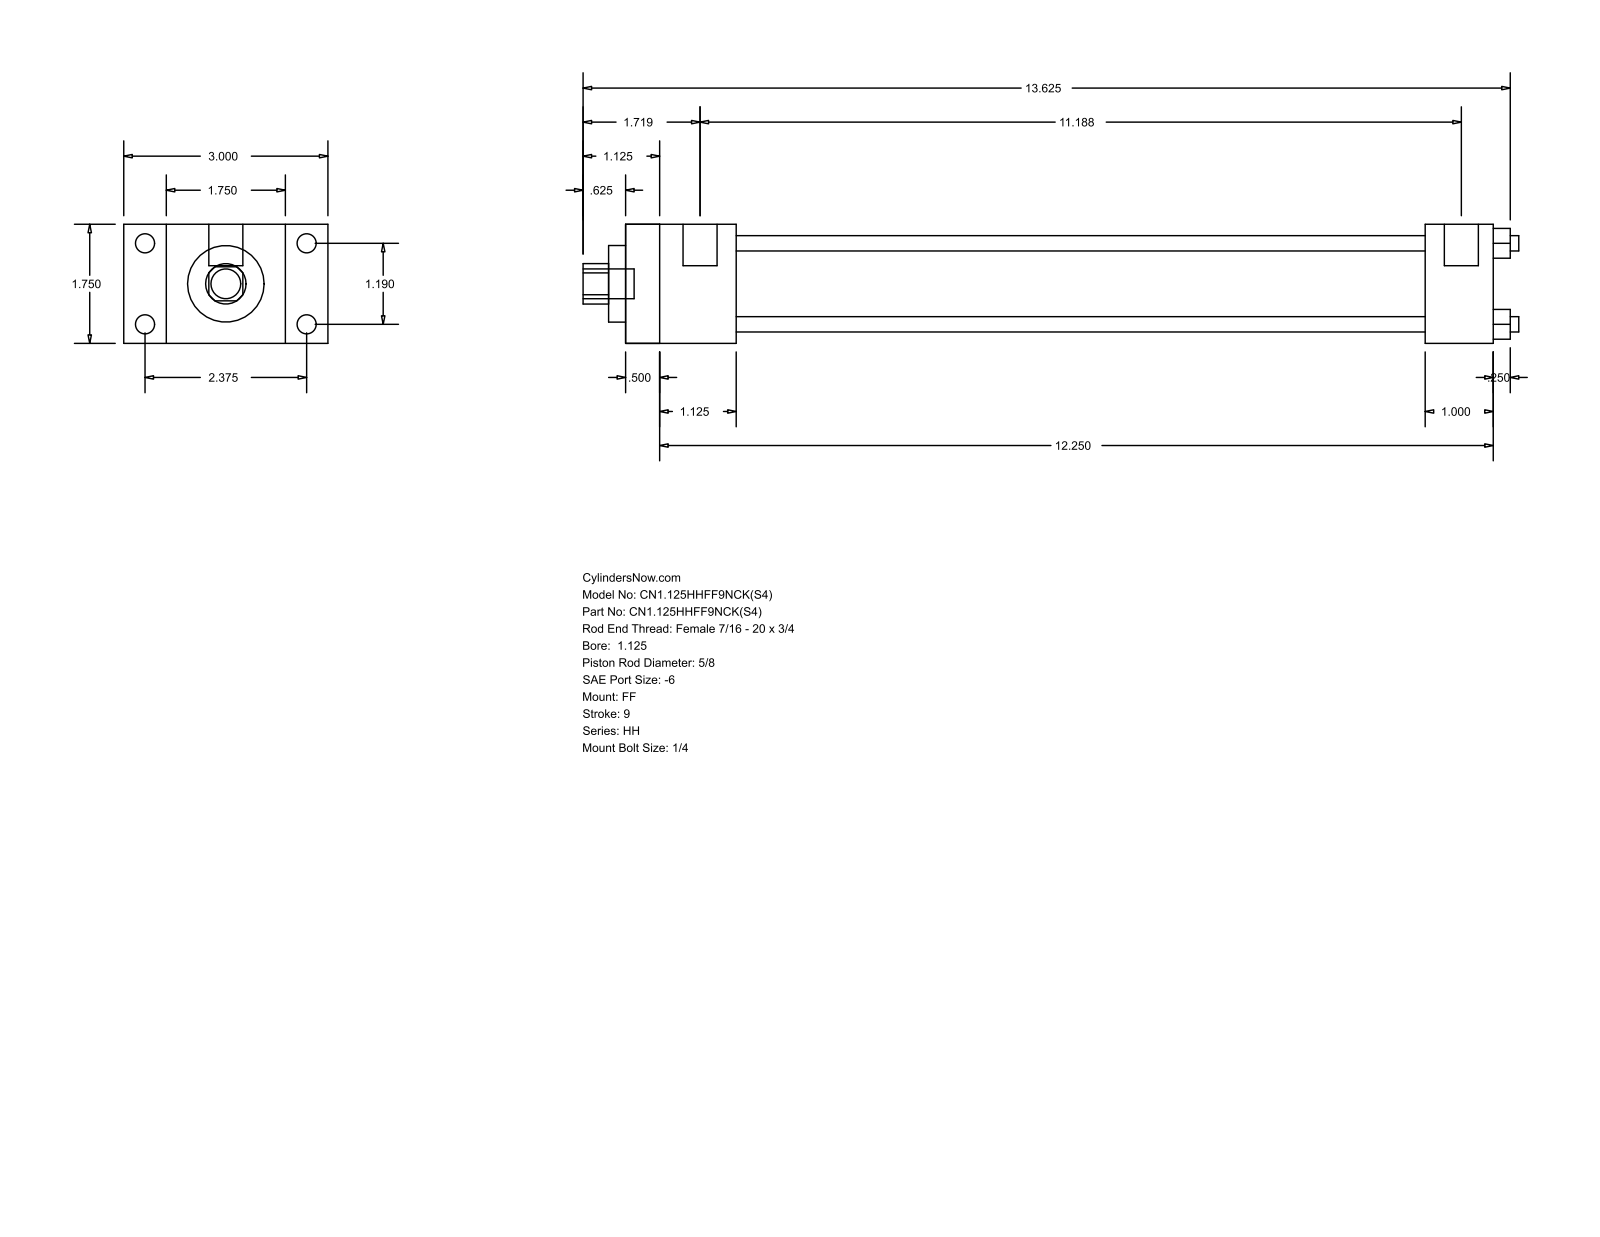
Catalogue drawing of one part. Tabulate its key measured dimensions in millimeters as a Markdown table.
| quantity | value |
| --- | --- |
| part name | HH_FF__0112_0.625 |
| STEP written by | GSSL Pune (CONFIG_CONTROL_DESIGN) |
| units | millimeters |
| bodies | 0 solids, 92 faces (64 planar, 28 cylindrical, 0 other) |
| overall size | 349.25 × 76.2 × 44.45 |
| round holes (diameter × count) | 5.71 × 4, 15.88 × 1, 28.57 × 1, 34.92 × 1 |
| round bosses / shafts (diameter × count) | 7.14 × 4, 5.56 × 4, 12.7 × 2, 11.11 × 1 |
| partial cylindrical surfaces (radius × count) | 7.54 × 1 |
| main face-to-face distances | 44.46, 323.85, 15.87, 12.69, 311.16, 60.33, 28.58, 41.27, 298.44, 285.75 |
| hole center spacings | 21.37, 30.22, 42.74 |
